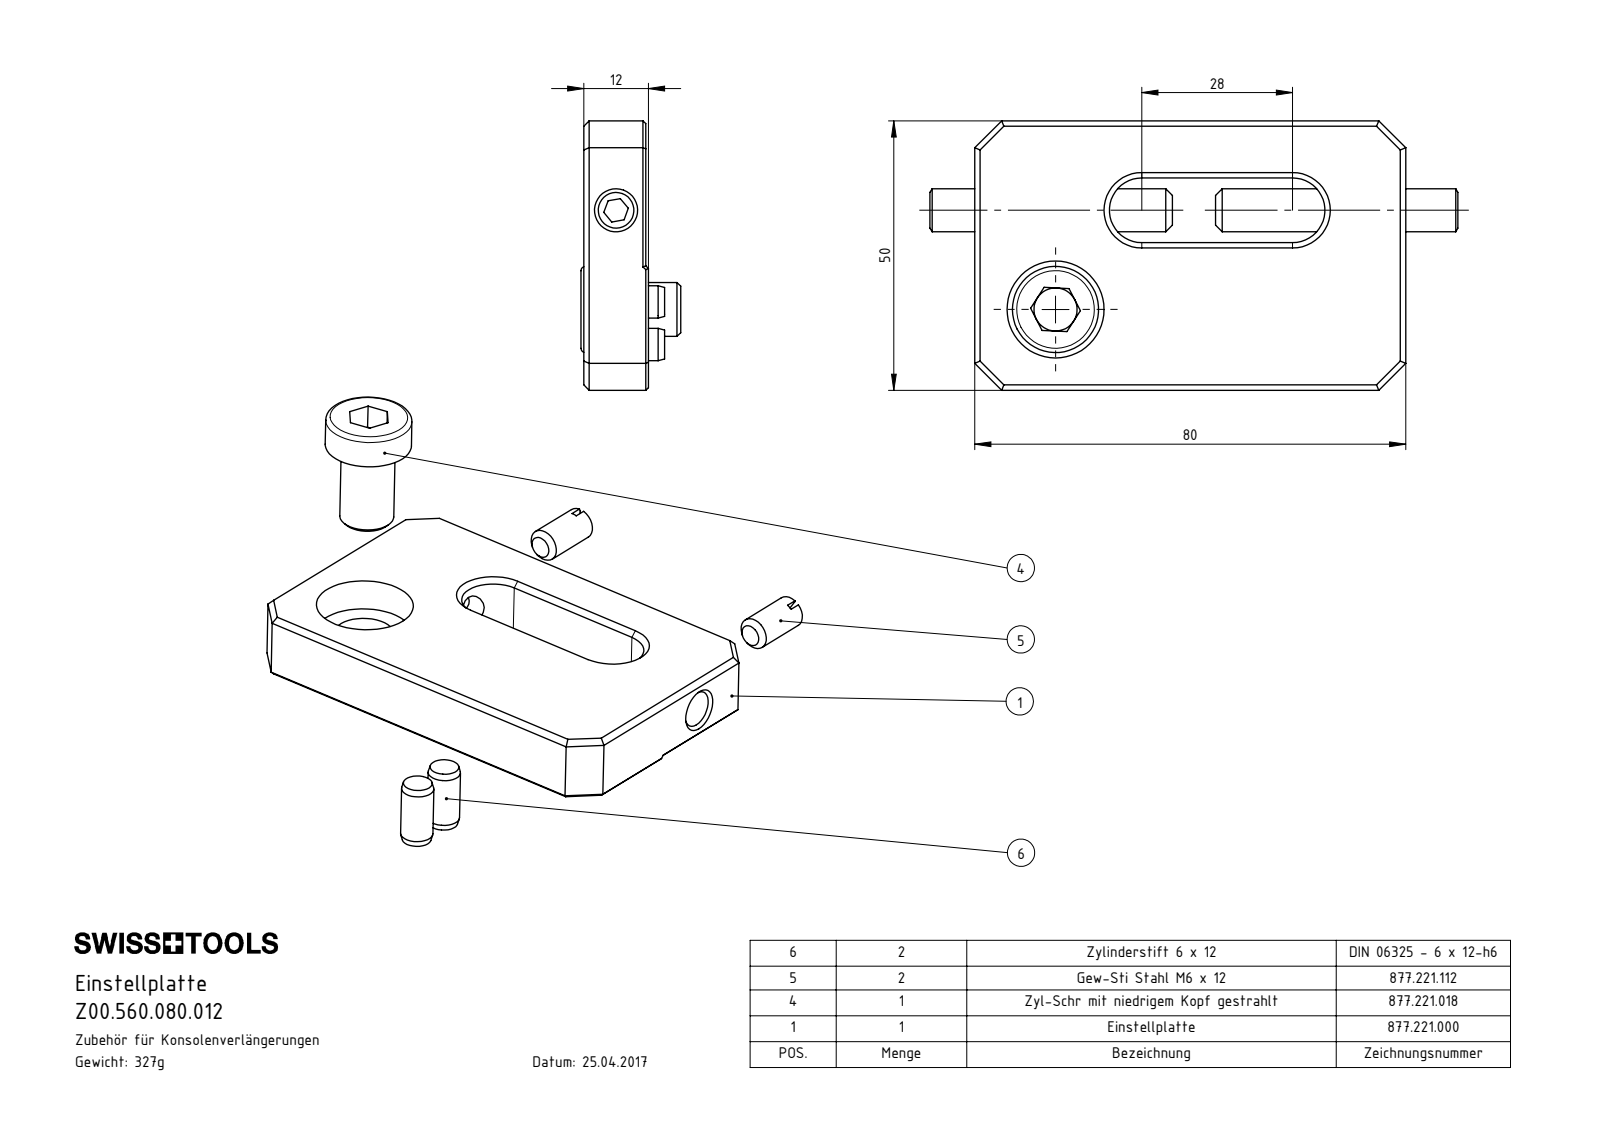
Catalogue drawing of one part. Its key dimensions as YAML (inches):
part_name: "ISO 4766 - M6x12_ISO 4766 - M6 x 10; ISO 4026 - M8 x 45; DIN 6912 - M10 x 12; ISO 8734 - 6 x 12 (+2 more)"
step_written_by: "SolidWorks 2022 (AUTOMOTIVE_DESIGN)"
units: inches
bodies: {solids: 8, faces: 168, planar: 86, cylindrical: 35, other: 47}
overall_size: [3.858, 1.969, 0.728]
volume: 2.682
surface_area: 26.88
round_holes:
  - {diameter: 0.197, count: 2}
  - {diameter: 0.236, count: 2}
  - {diameter: 0.268, count: 1}
  - {diameter: 0.433, count: 1}
  - {diameter: 0.709, count: 1}
round_bosses_or_shafts:
  - {diameter: 0.236, count: 2}
  - {diameter: 0.63, count: 1}
  - {diameter: 0.394, count: 1}
  - {diameter: 0.315, count: 1}
partial_cylinders:
  - {radius: 0.236, count: 2}
face_to_face_distances: [0.472, 0.02, 0.453, 1.969, 0.236, 3.15, 0.417, 1.551, 1.079, 0.89]
hole_center_spacings: [0.311, 0.73, 0.772, 1.969]
